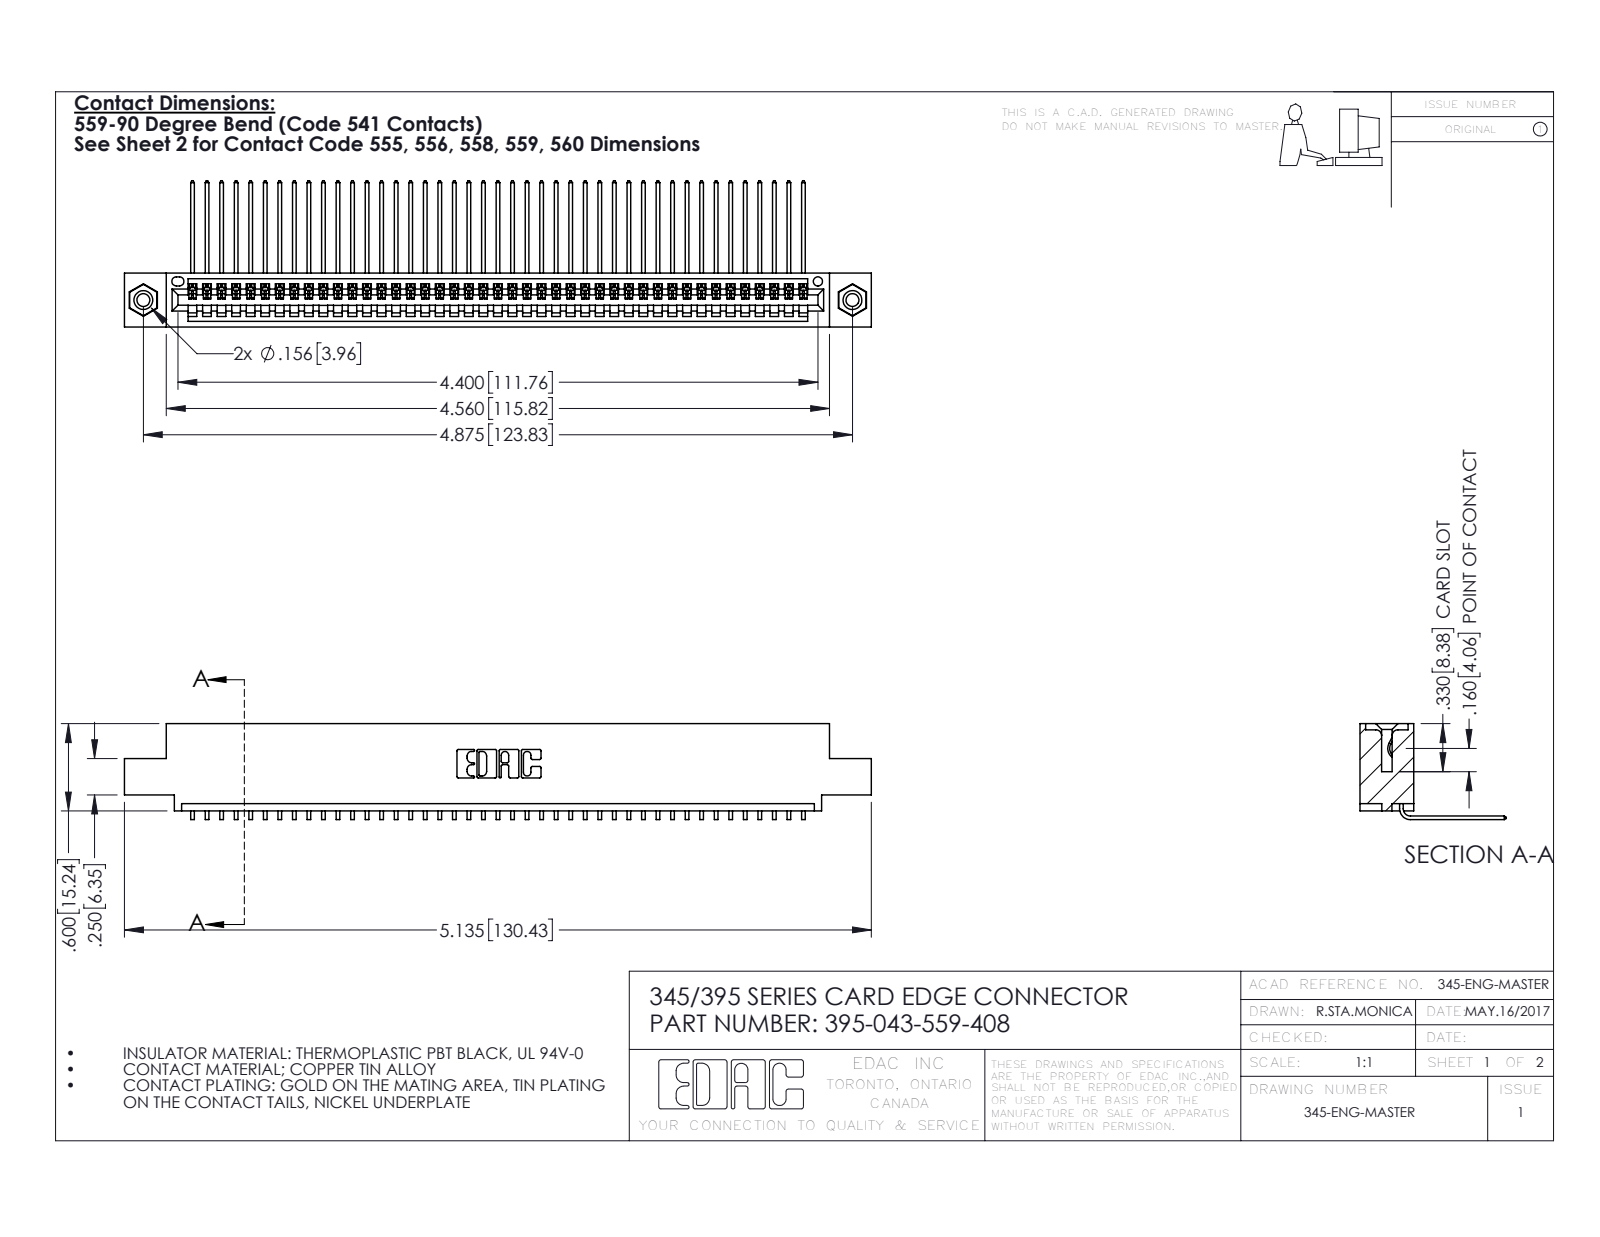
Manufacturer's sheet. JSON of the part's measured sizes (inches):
{"part_name": "345-250-001_345-250-003-102; 345-292-001_558 559 Tail - 1; 395-043-559-408; 345 Part_0.110 Offset - 0.156 Dia-TI", "step_written_by": "SolidWorks 2016 (CONFIG_CONTROL_DESIGN)", "units": "inches", "bodies": {"solids": 46, "faces": 2770, "planar": 1922, "cylindrical": 832, "other": 16}, "overall_size": [5.135, 1.005, 0.659], "volume_in3": 0.76, "surface_area_in2": 27.15, "round_holes": [[0.089, 2], [0.125, 2], [0.156, 2], [0.064, 1]], "round_bosses_or_shafts": [[0.155, 2]], "partial_cylinders_radius": [[0.006, 86], [0.01, 22], [0.007, 6], [0.031, 6], [0.026, 3], [0.031, 2], [0.04, 2], [0.014, 1]], "face_to_face_distances": [0.072, 0.298, 0.37, 0.2, 0.098, 0.272, 0.025, 0.225, 0.149, 0.072], "hole_center_spacings": [0.27, 4.639, 4.875]}
